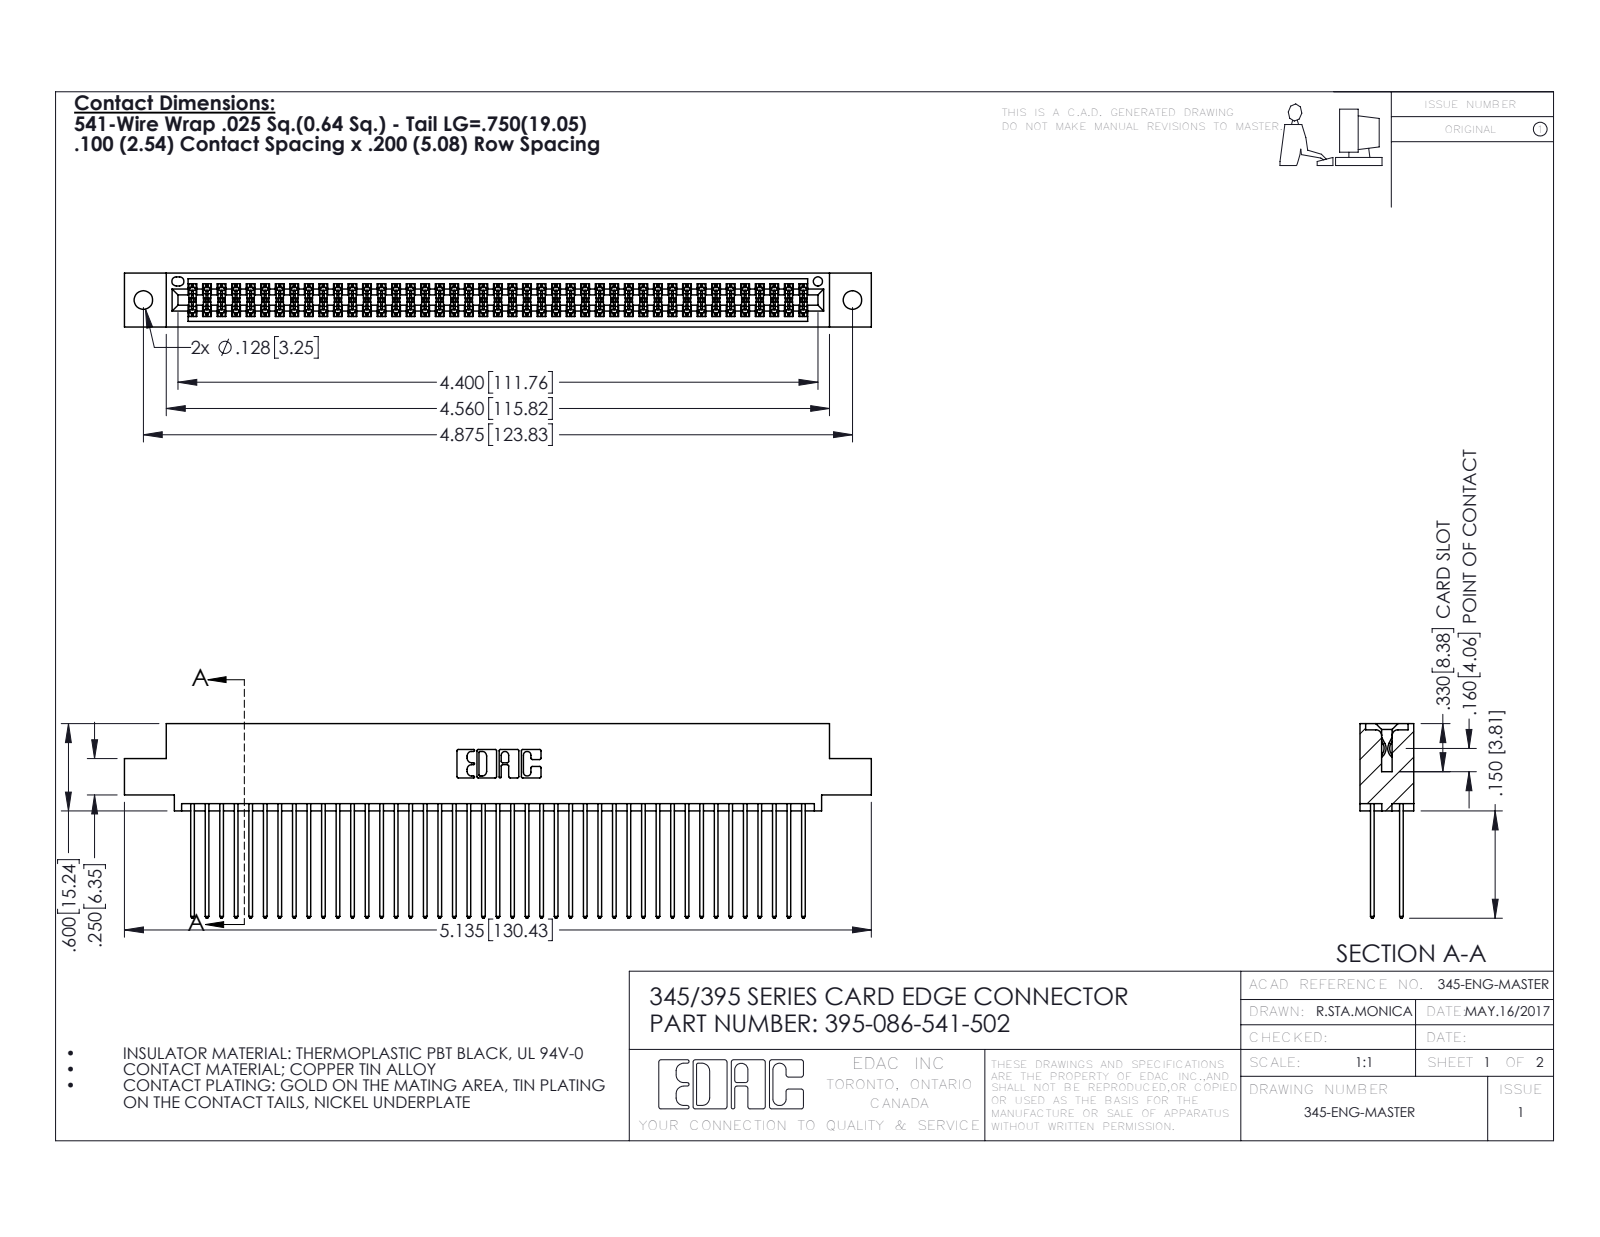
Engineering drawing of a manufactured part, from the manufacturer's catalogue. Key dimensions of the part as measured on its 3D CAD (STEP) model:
Part name (STEP PRODUCT): 395-086-541-502; 345-292-001_345-293-141; 345 Part_0.110 Offset - 0.128 Dia
STEP written by: SolidWorks 2016 (CONFIG_CONTROL_DESIGN)
Units: inches
Bodies: 87 solids, 4430 faces (2922 planar, 1508 cylindrical, 0 other)
Overall size (bounding box): 5.135 × 1.337 × 0.37
Volume: 0.797 in³ · Surface area: 33.27 in²
Round holes (diameter × count): ⌀0.128 ×2, ⌀0.064 ×1
Partial cylindrical surfaces — rounded edges, fillets, slot ends (radius × count): R0.006 ×129, R0.01 ×86, R0.01 ×22, R0.007 ×6, R0.031 ×6, R0.026 ×3, R0.014 ×2, R0.019 ×2
Main face-to-face distances: 0.298, 0.072, 0.2, 0.098, 0.272, 0.025, 0.225, 0.37, 0.175, 0.149
Hole centre spacings: 0.27, 4.639, 4.875
